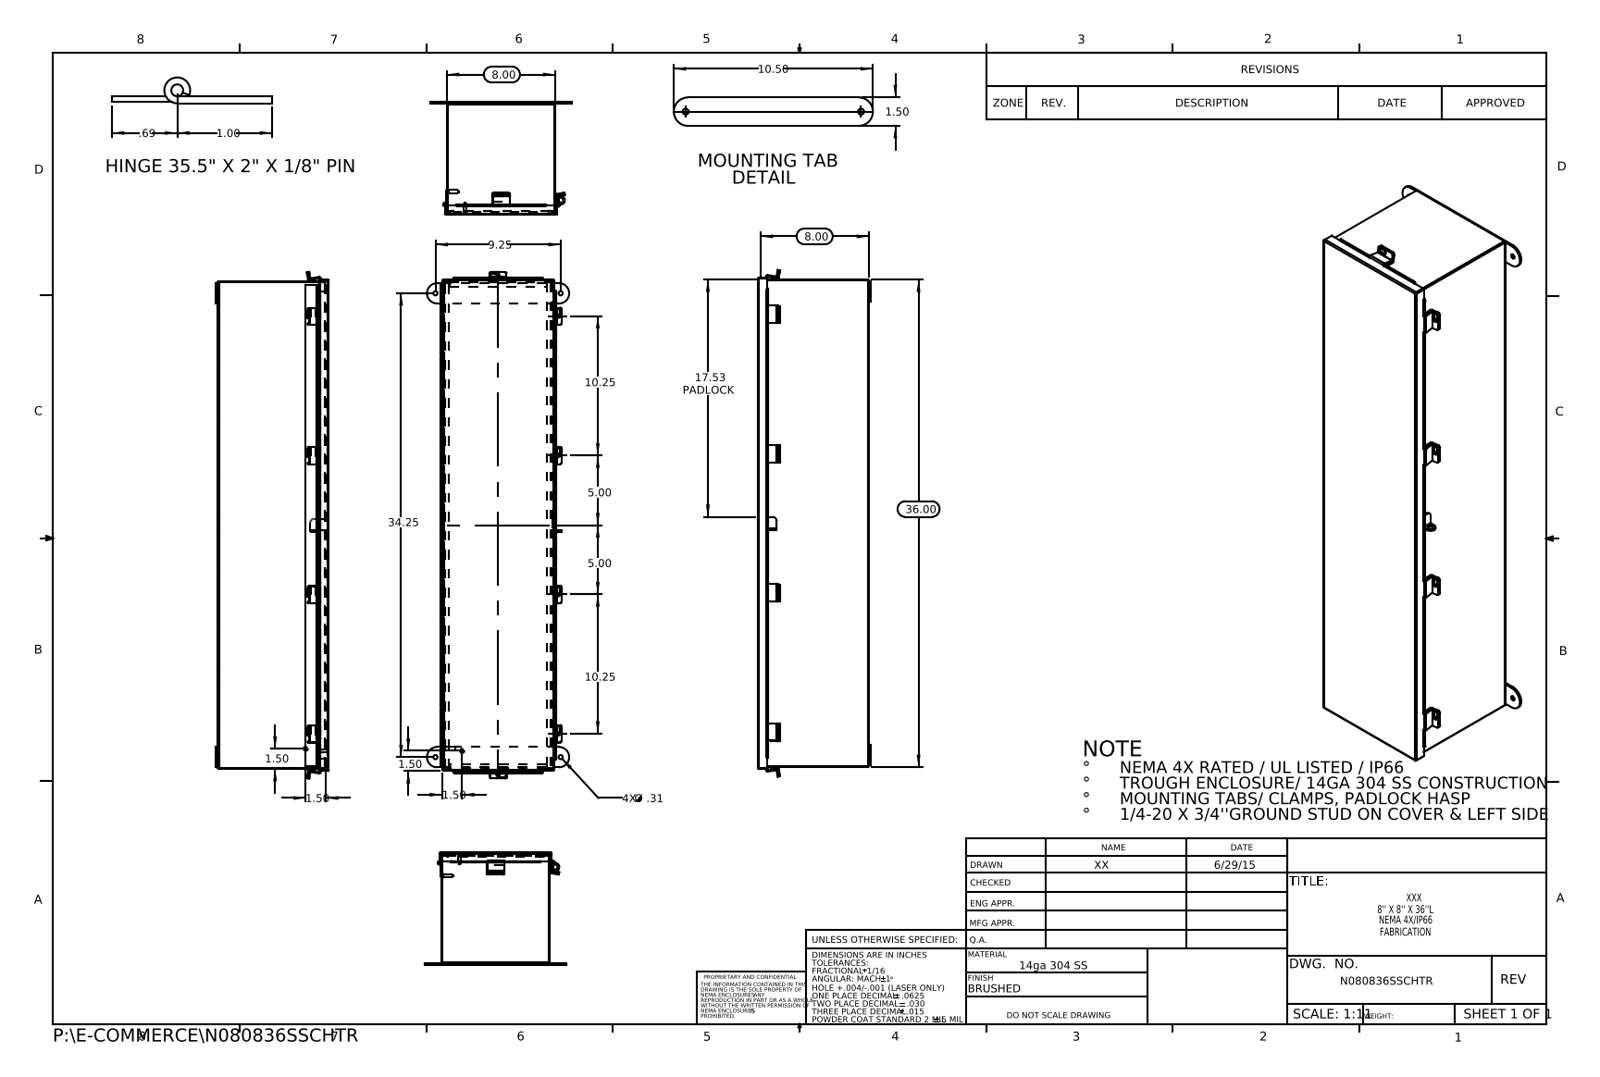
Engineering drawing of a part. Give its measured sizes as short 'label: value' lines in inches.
name: N080836SSCHTR JIC Clamp Bracket; N080836SSCHTR JIC Bottom; N080836SSCHTR Hinge Body Side; N080836SSCHTR (+8 more)
written by: SolidWorks 2015 (CONFIG_CONTROL_DESIGN)
unit: in
bodies: 23 solids, 1148 faces (697 planar, 431 cylindrical, 20 other)
size: 37.407 × 10.5 × 8.337
volume: 112.6 in³; area: 3 021 in²
holes: 6× ⌀0.25, 4× ⌀0.313, 1× ⌀0.125, 1× ⌀0.125, 1× ⌀0.375
bosses: 2× ⌀0.315, 2× ⌀0.236, 1× ⌀0.273, 1× ⌀0.25
rounds: 23× R0.125, 12× R0.009, 12× R0.133, 11× R0.013, 11× R0.088, 6× R0.083, 6× R0.1, 4× R0.75
face distances: 0.075, 7.925, 8.128, 8, 7.85, 8.203, 8.053, 35.925, 0.149, 8.074
hole spacings: 9.25, 10.287, 20.564, 34.25, 35.478, 8.541, 10.277, 30.85
